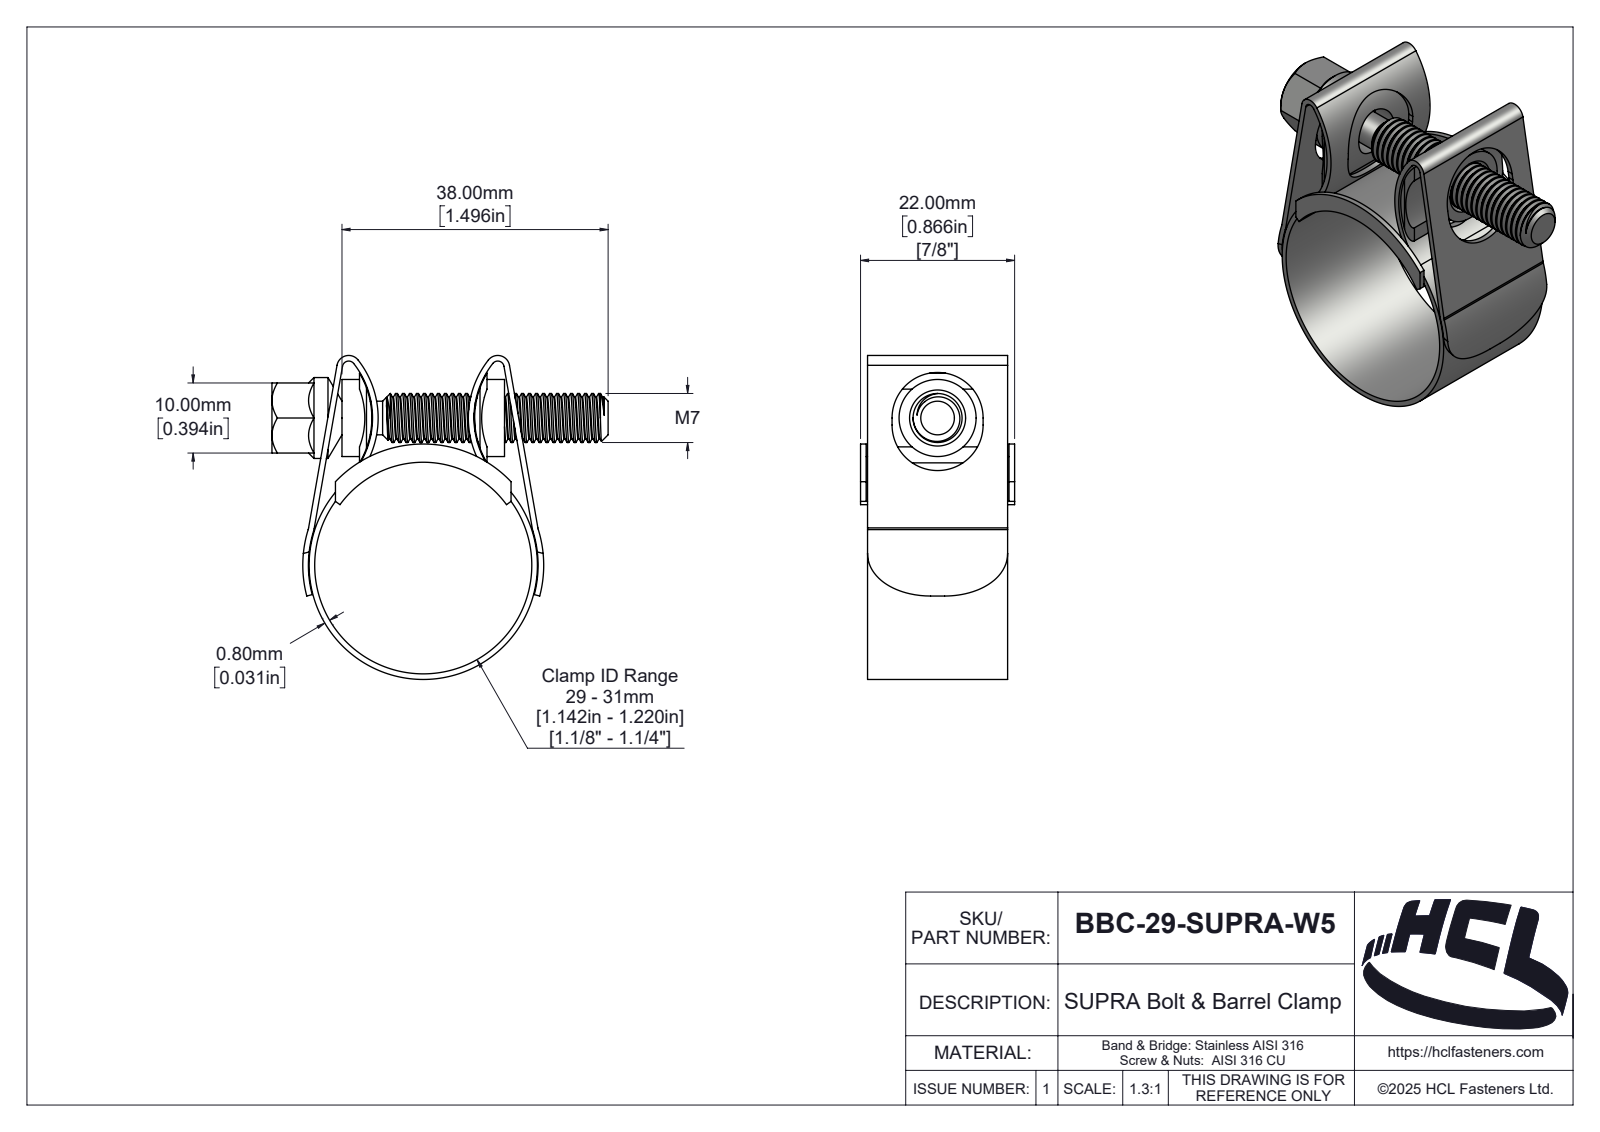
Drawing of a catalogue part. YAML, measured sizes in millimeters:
part_name: "BBC-29-SUPRA-W5"
step_written_by: "SolidWorks 2025 (AUTOMOTIVE_DESIGN)"
units: millimeters
bodies: {solids: 5, faces: 300, planar: 46, cylindrical: 174, other: 80}
overall_size: [48, 46.24, 22]
volume: 5729
surface_area: 11082
round_holes:
  - {diameter: 31, count: 1}
round_bosses_or_shafts:
  - {diameter: 11.55, count: 1}
  - {diameter: 11, count: 1}
  - {diameter: 7, count: 1}
  - {diameter: 4.8, count: 1}
partial_cylinders:
  - {radius: 1, count: 4}
  - {radius: 0.9, count: 2}
  - {radius: 1.7, count: 2}
  - {radius: 2, count: 2}
  - {radius: 2.8, count: 2}
  - {radius: 6.5, count: 2}
  - {radius: 11.49, count: 2}
  - {radius: 12.49, count: 2}
face_to_face_distances: [0.8, 1, 21, 20, 10, 20.7, 21.2, 20.2, 2.5, 22]
